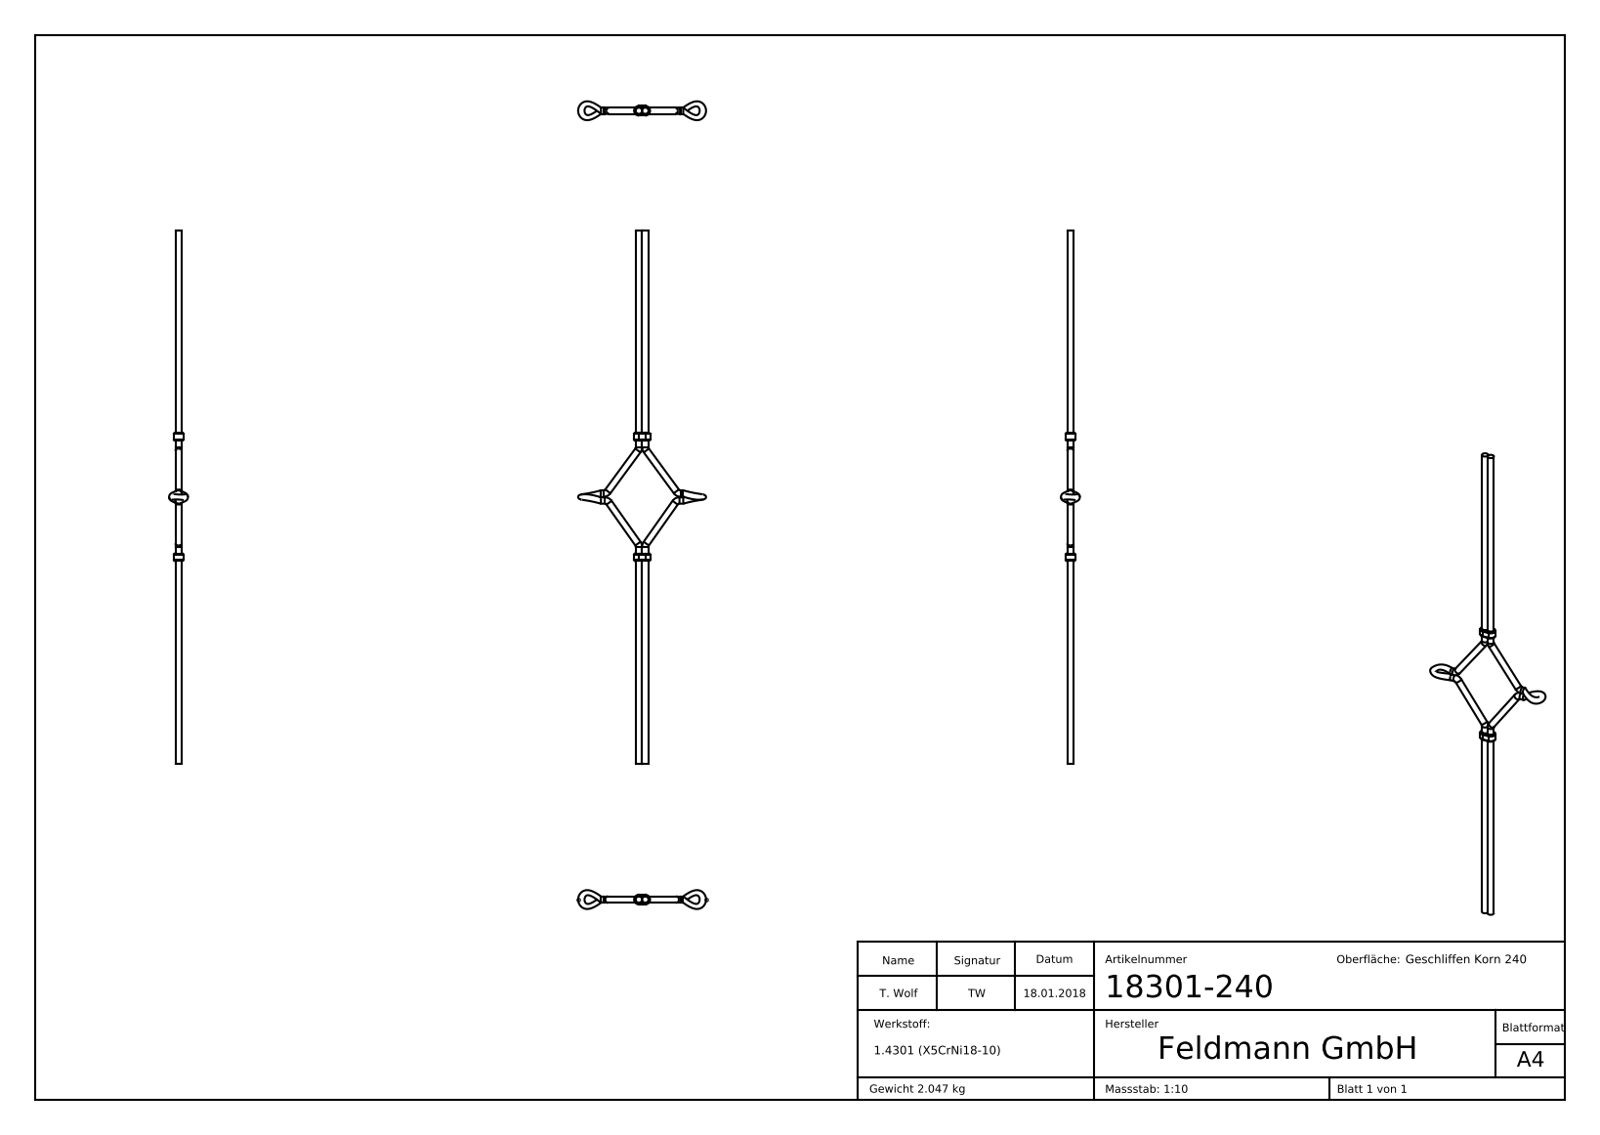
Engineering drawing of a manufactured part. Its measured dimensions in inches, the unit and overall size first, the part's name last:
Units: inches
Overall size (bounding box): 39.37 × 9.45 × 1.393
Round holes (diameter × count): ⌀0.472 ×2
Round bosses / shafts (diameter × count): ⌀0.472 ×6
Partial cylindrical surfaces — rounded edges, fillets, slot ends (radius × count): R0.079 ×8, R0.354 ×2
Main face-to-face distances: 0.118, 0.591, 0.472, 0.709, 39.37, 14.961, 15.512, 23.858, 24.409, 8.898
Hole centre spacings: 0.472
Volume: 15.77 in³ · Surface area: 140.1 in²
Bodies: 4 solids, 323 faces (154 planar, 28 cylindrical, 141 other)
Part name (STEP PRODUCT): 18301-240 Teil2_18301-240 Teil2; 18301-240 Teil1_18301-240 Teil1; 18301-240 Teil2; 18301-240 Teil3 (+3 more)
STEP written by: SolidWorks 2018 (CONFIG_CONTROL_DESIGN)
